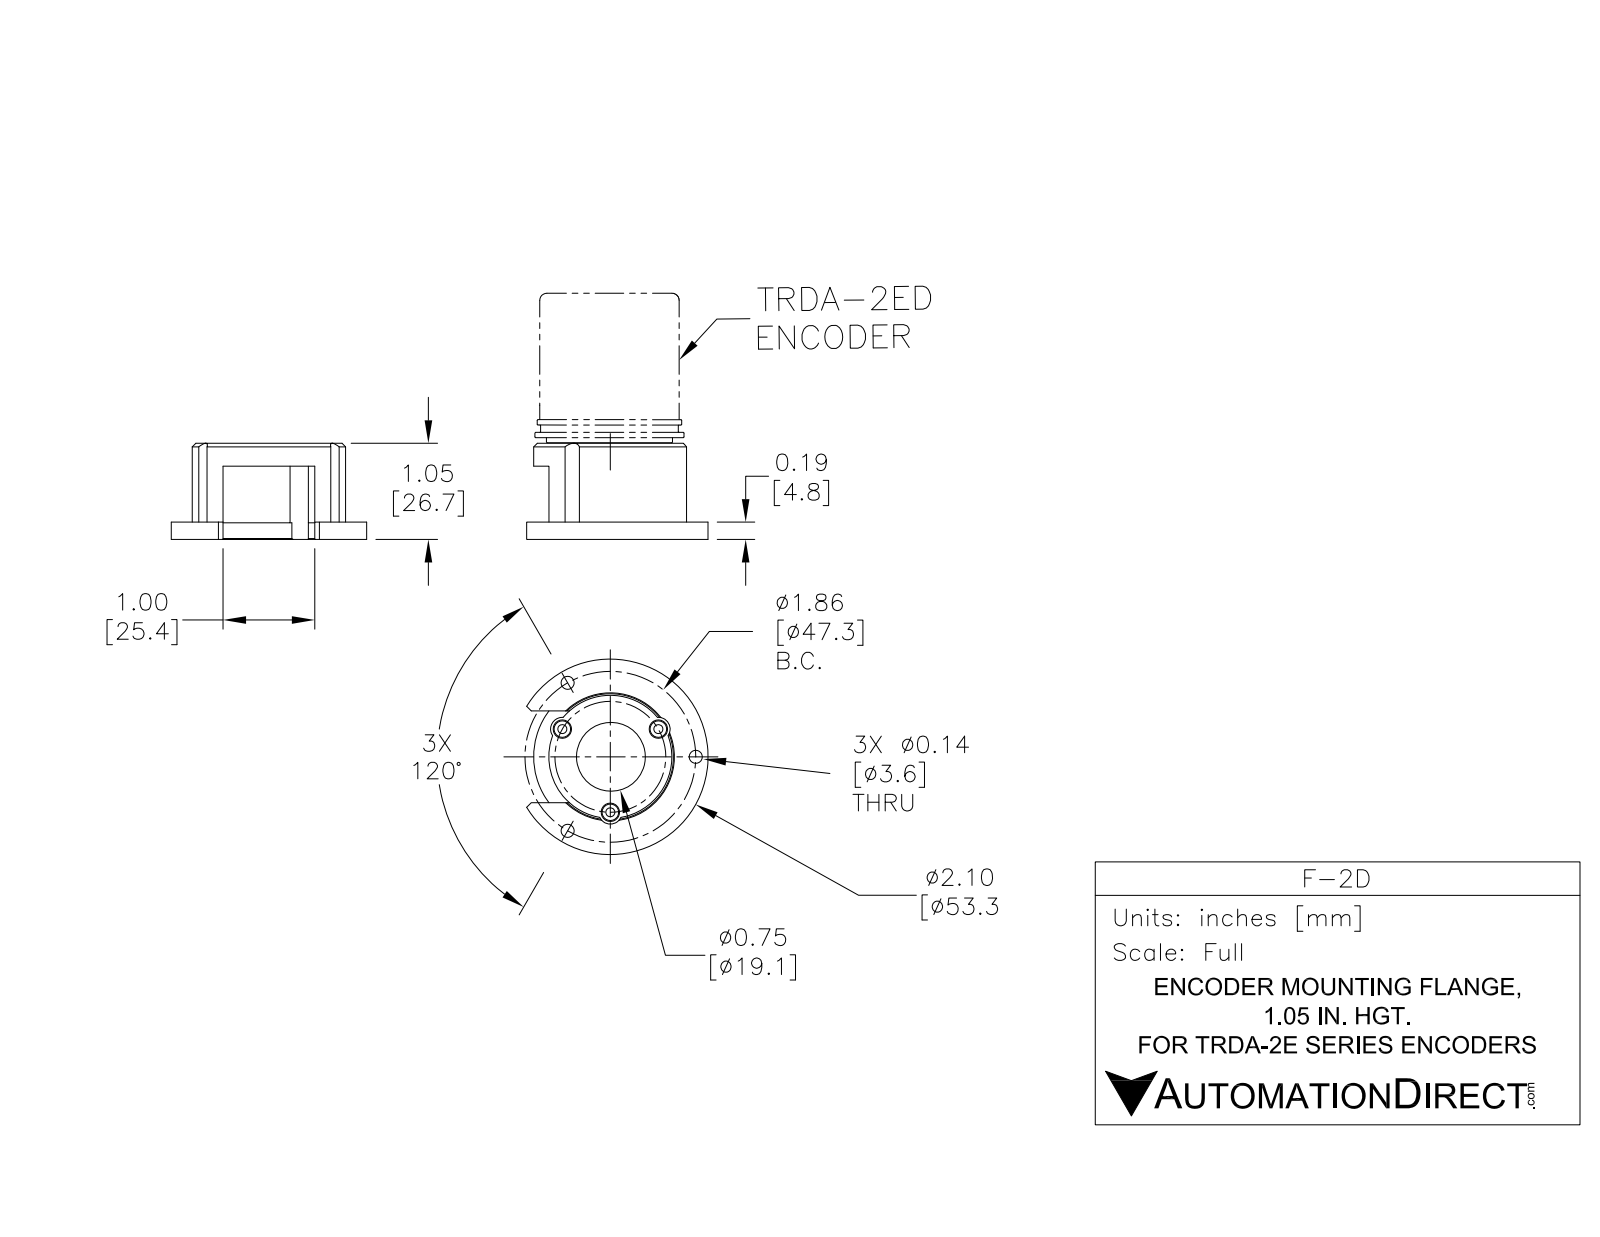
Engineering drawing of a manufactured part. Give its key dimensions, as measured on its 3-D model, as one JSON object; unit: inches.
{"part_name": "F-2D", "step_written_by": "SolidWorks 2016 (AUTOMOTIVE_DESIGN)", "units": "inches", "bodies": {"solids": 1, "faces": 68, "planar": 21, "cylindrical": 38, "other": 9}, "overall_size": [2.098, 1.936, 1.05], "volume_in3": 0.963, "surface_area_in2": 14.42, "round_holes": [[0.256, 6], [0.126, 3], [0.14, 3], [0.75, 1], [1.34, 1]], "round_bosses_or_shafts": [[2.098, 1], [1.68, 1]], "partial_cylinders_radius": [[0.687, 1]], "face_to_face_distances": [1.05, 0.19, 0.86, 0.908, 0.718, 0.142, 0.02, 0.738, 1, 0.8], "hole_center_spacings": [0.605, 0.931, 1.048, 1.613, 0.507, 1.11, 1.486, 0.507]}
